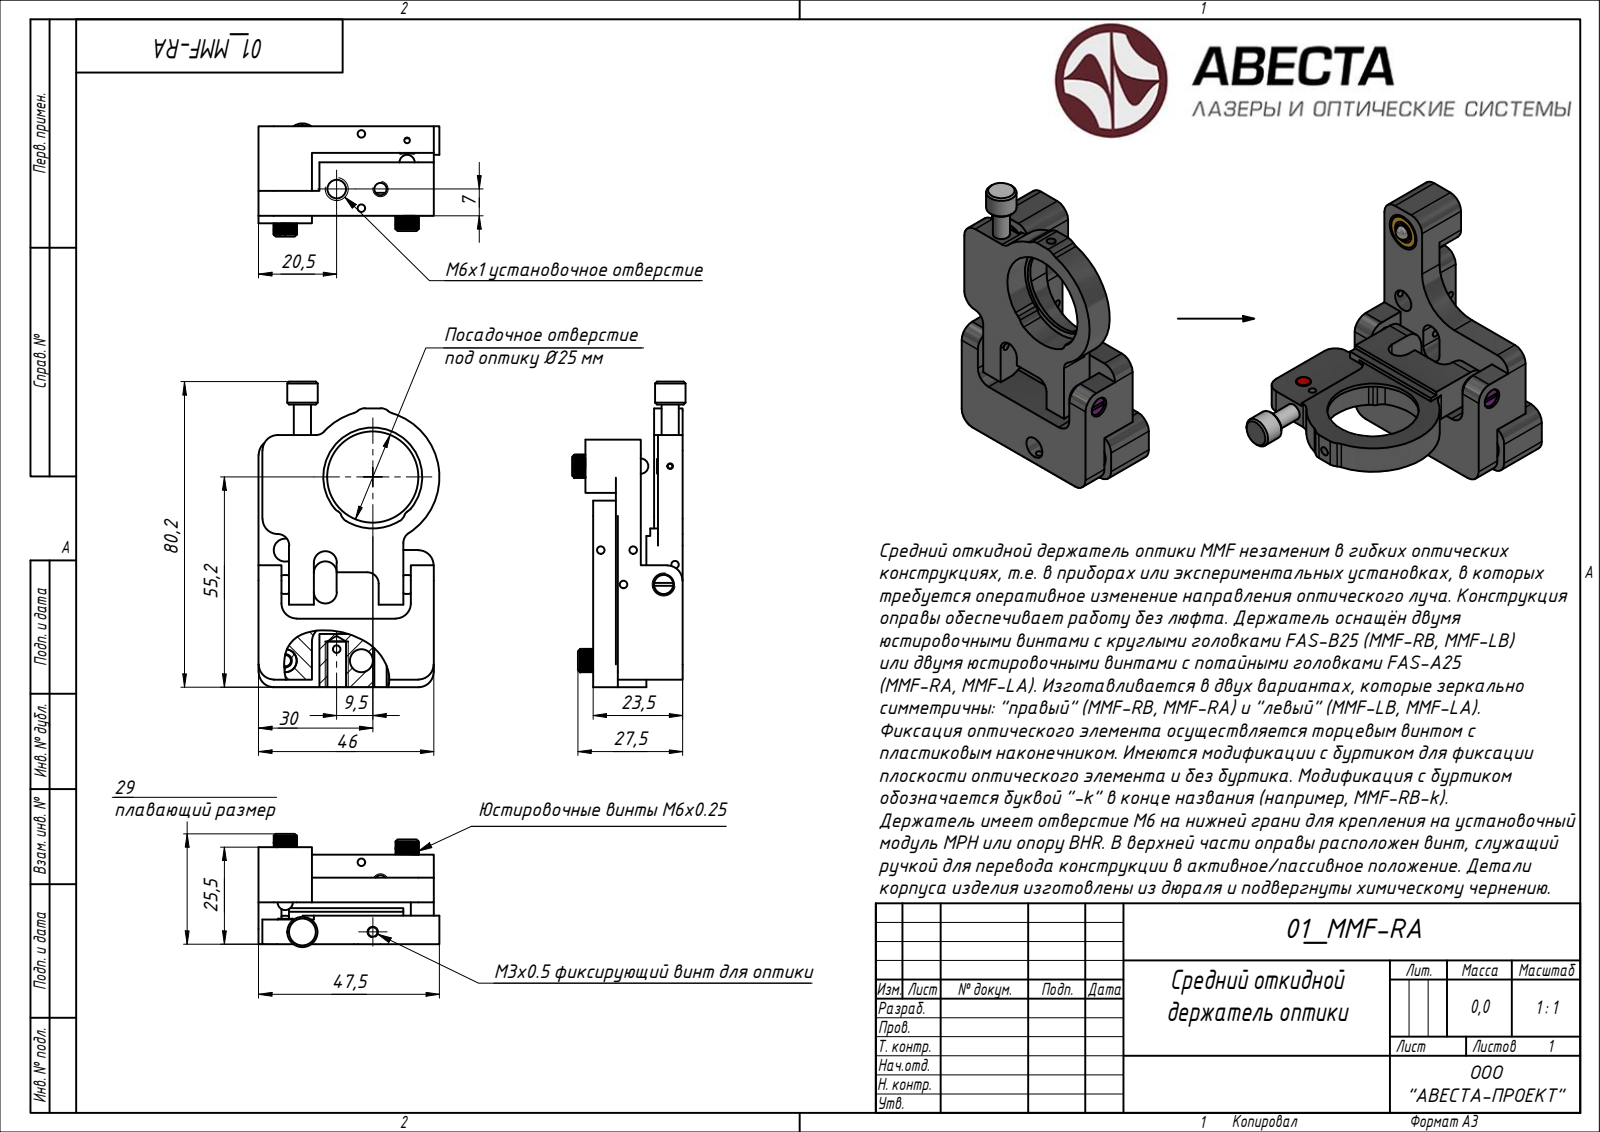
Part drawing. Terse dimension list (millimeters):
written by: ST-DEVELOPER v15 (AUTOMOTIVE_DESIGN)
unit: mm
bodies: 16 solids, 412 faces (133 planar, 0 cylindrical, 279 other)
size: 80.2 × 47.5 × 27.95
volume: 37 242 mm³; area: 22 427 mm²
face distances: 6.5, 6, 2, 14, 0.5, 11, 16, 17.5, 8, 23.5
